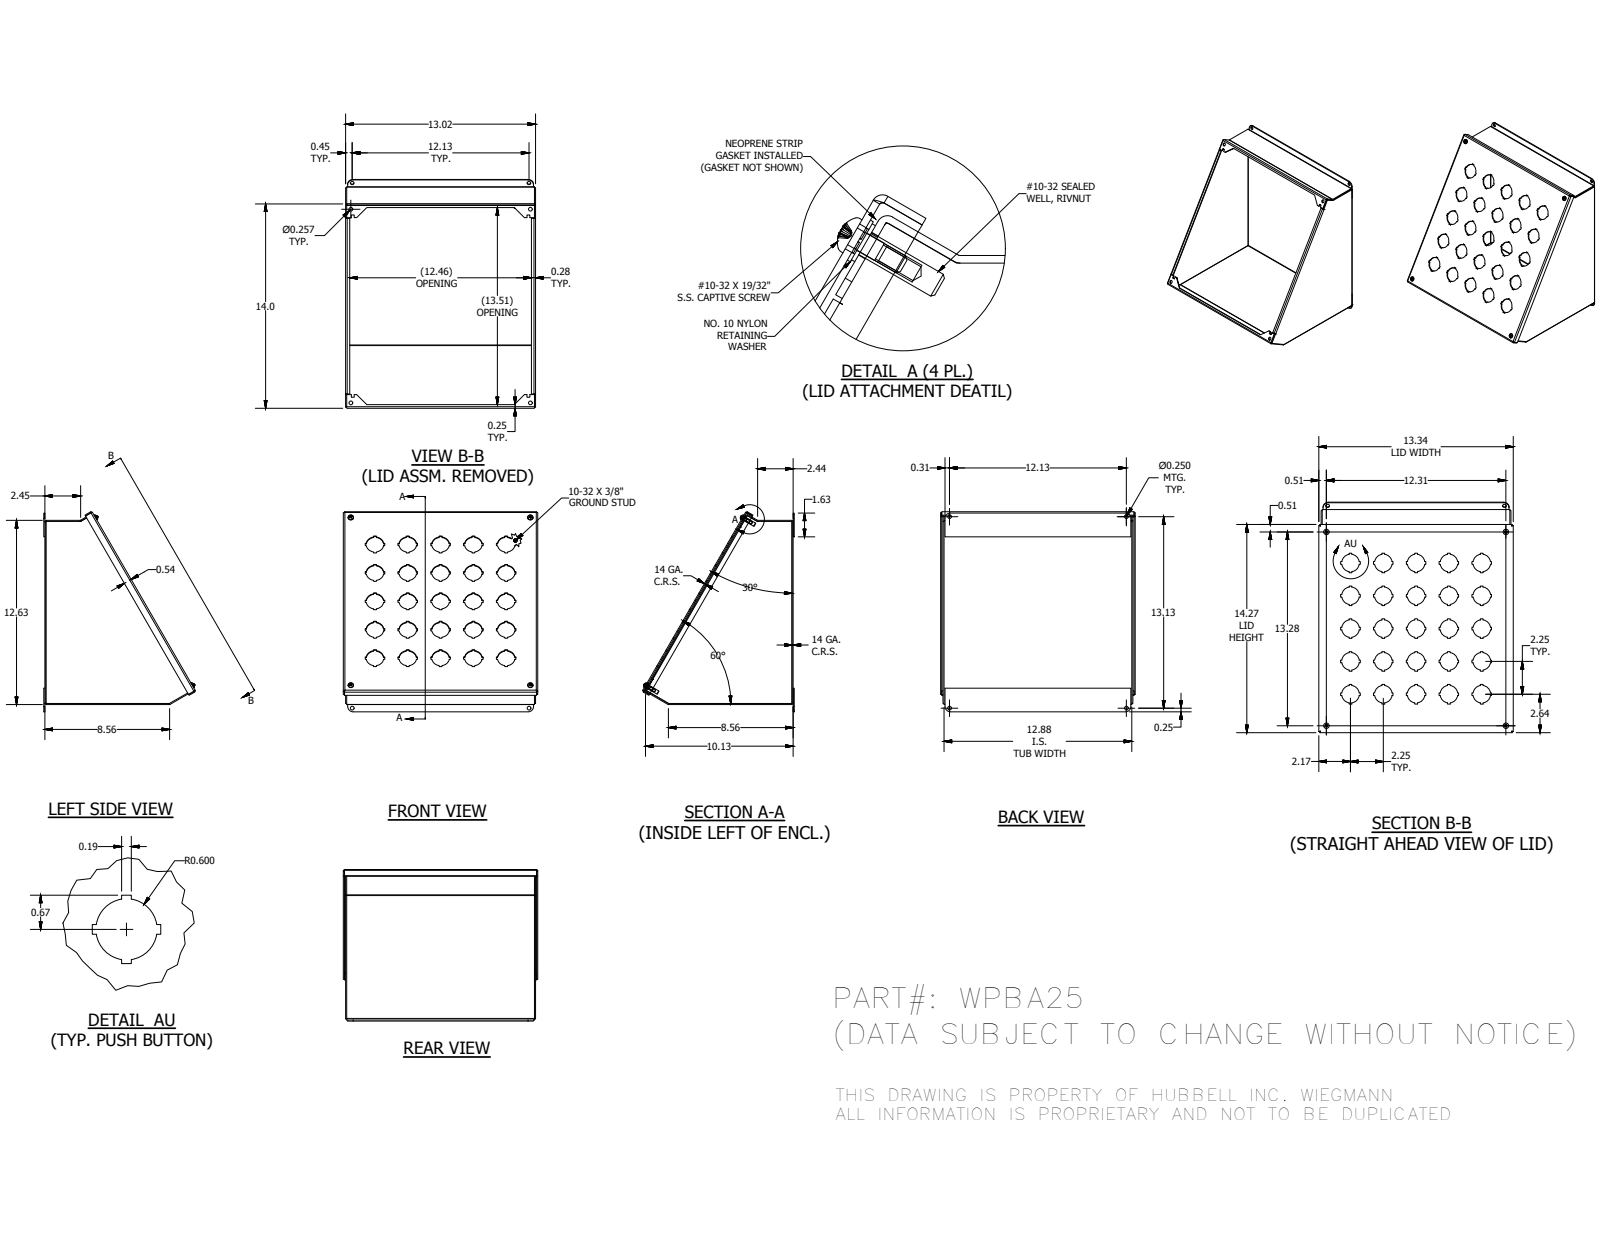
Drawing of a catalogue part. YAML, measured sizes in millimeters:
part_name: "WPBA25BKP; WPBA5ROWEWPR; WPBA5ROWEWPL; 34984 (+6 more)"
step_written_by: "Autodesk Inventor 2014 (AUTOMOTIVE_DESIGN)"
units: millimeters
bodies: {solids: 19, faces: 880, planar: 591, cylindrical: 190, other: 99}
overall_size: [348.57, 338.76, 263.92]
volume: 907004
surface_area: 985934
round_holes:
  - {diameter: 30.48, count: 25}
  - {diameter: 3.96, count: 4}
  - {diameter: 4.98, count: 4}
  - {diameter: 6.35, count: 4}
  - {diameter: 6.53, count: 4}
  - {diameter: 7.06, count: 4}
  - {diameter: 7.14, count: 4}
round_bosses_or_shafts:
  - {diameter: 4.83, count: 5}
  - {diameter: 11.51, count: 4}
  - {diameter: 10.31, count: 4}
  - {diameter: 9.47, count: 4}
  - {diameter: 6.3, count: 4}
  - {diameter: 6.35, count: 1}
partial_cylinders:
  - {radius: 0.79, count: 12}
  - {radius: 2.67, count: 12}
  - {radius: 2.27, count: 4}
  - {radius: 9.53, count: 4}
face_to_face_distances: [1.88, 1.87, 328.9, 328.91, 327.03, 330.78, 318.92, 3.76, 317.04, 320.8]
hole_center_spacings: [127.79, 57.15, 80.82, 114.3, 171.45, 180.73, 206.05, 161.64]
